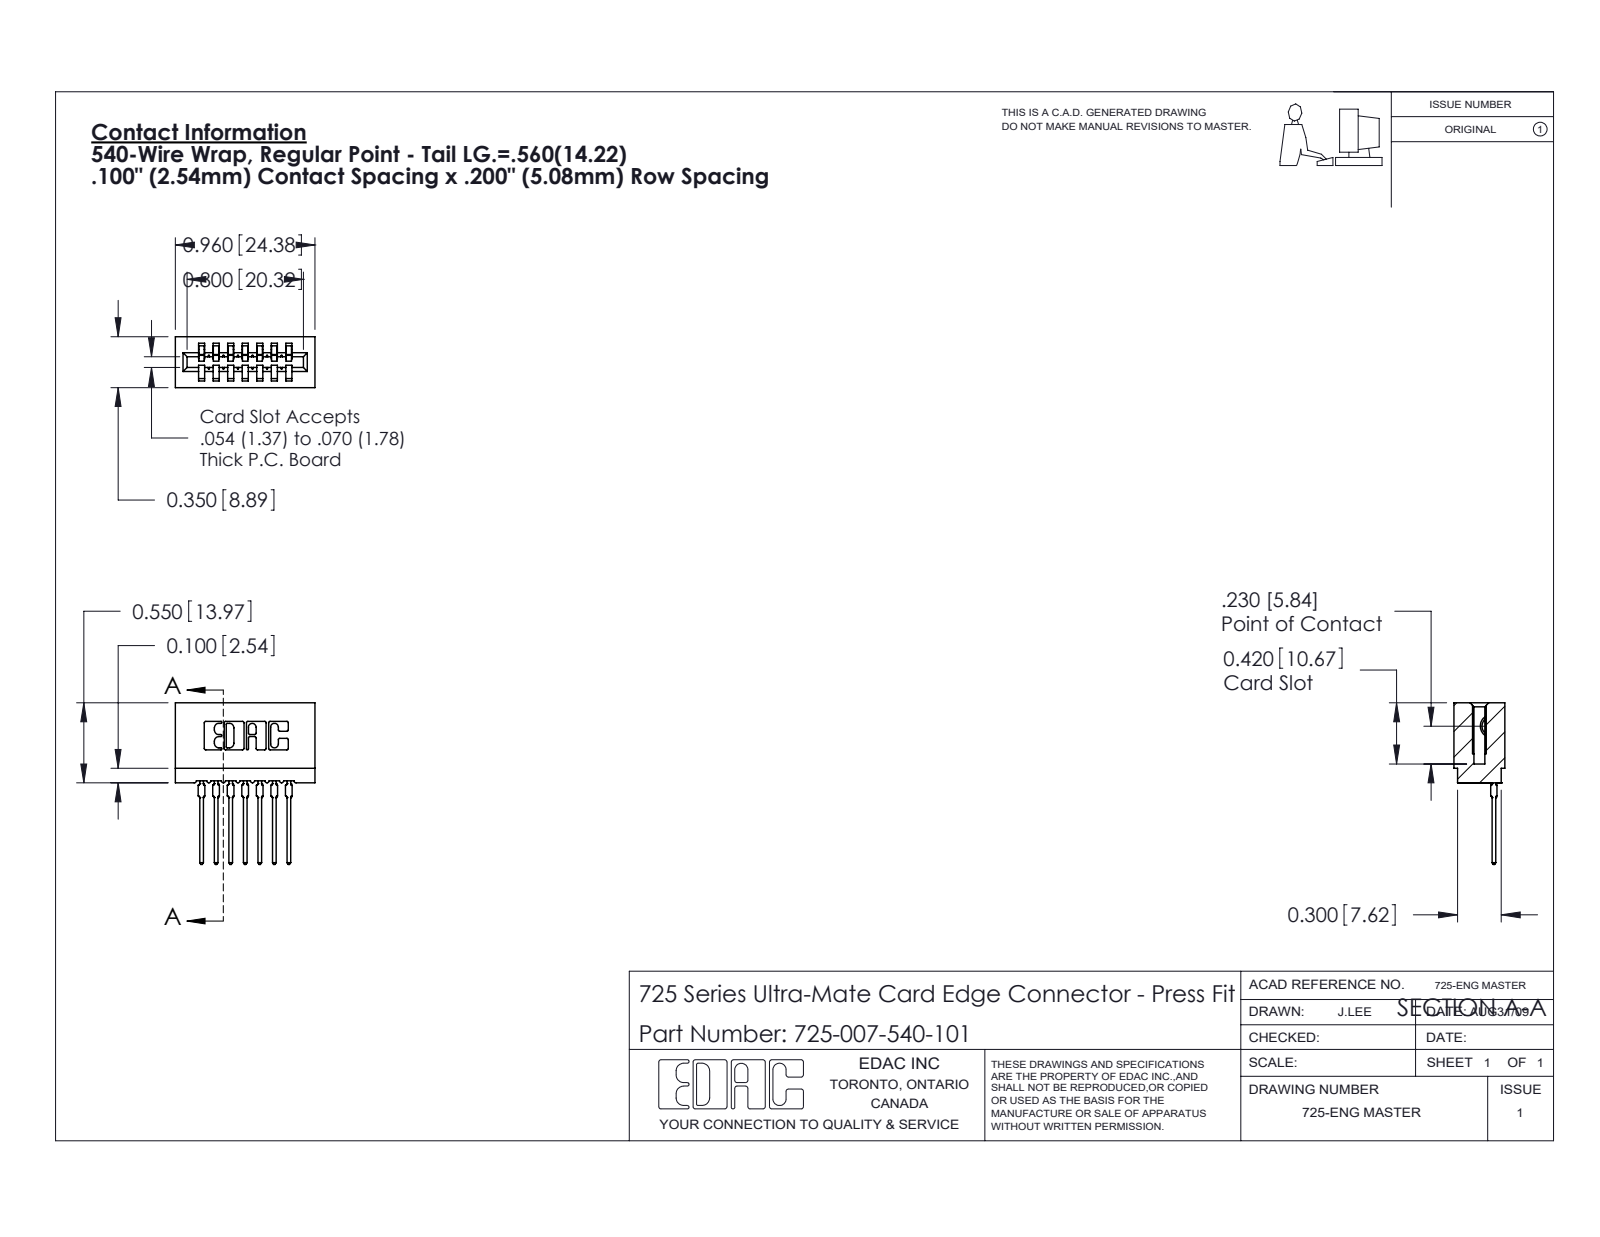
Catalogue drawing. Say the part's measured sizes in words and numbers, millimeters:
The part is named "725-007-540-101; 725 Part_Insulator Option - 01; 745-292-001_540". Its 3-D file was written by "SolidWorks 2020 (CONFIG_CONTROL_DESIGN)". It is 8 solids with 879 faces: 524 planar, 173 cylindrical and 182 other. Overall it measures 28.2 by 24.4 by 8.9 millimeters. Its volume is 2 060 cubic millimeters and its surface area 3 412 square millimeters. Partial cylindrical surfaces (rounded edges, fillets, slot ends): 22 of radius 0.3, 14 of radius 0.4, 14 of radius 0.5, 6 of radius 0.2, 6 of radius 0.8, 4 of radius 0.1, 4 of radius 0.3, 3 of radius 0.7. The main face-to-face distances are 2.5, 5.1, 7.6, 1.1, 10.2, 3.6, 1.5, 6.1, 4, 12.7.
